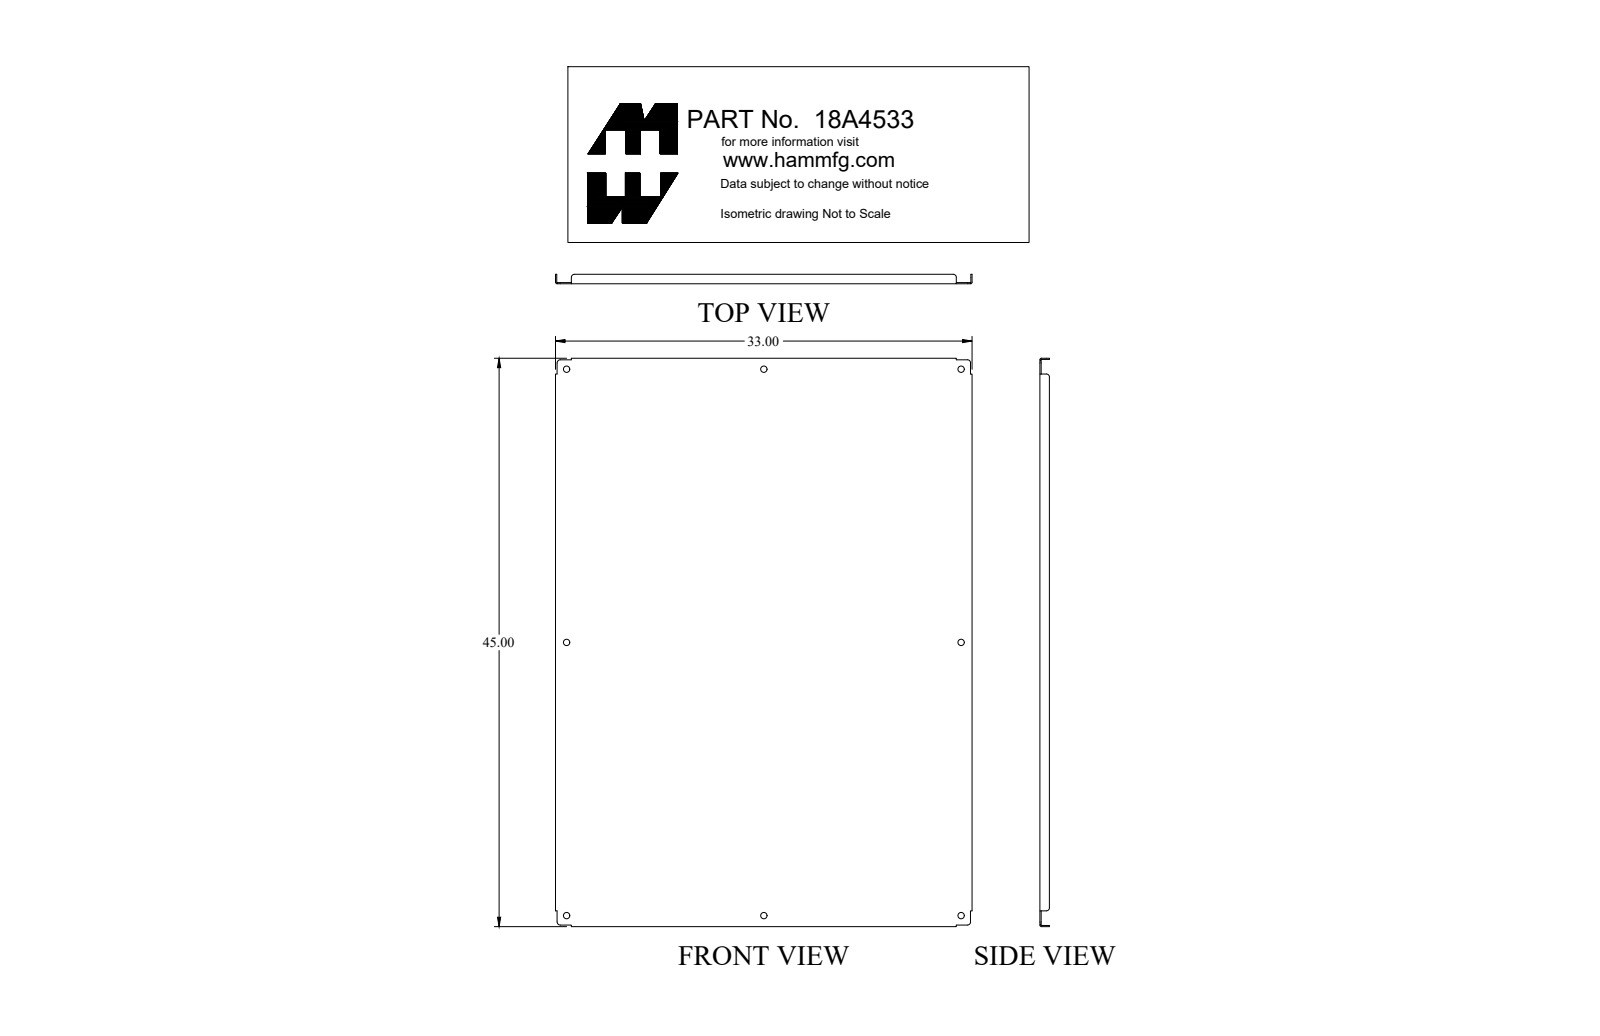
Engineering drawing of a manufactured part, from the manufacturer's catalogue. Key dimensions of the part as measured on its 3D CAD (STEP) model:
Part name (STEP PRODUCT): 18A4533
STEP written by: SolidWorks 2018 (AUTOMOTIVE_DESIGN)
Units: inches
Bodies: 1 solid, 58 faces (30 planar, 28 cylindrical, 0 other)
Overall size (bounding box): 45 × 33 × 0.75
Volume: 149.4 in³ · Surface area: 3 162 in²
Round holes (diameter × count): ⌀0.5 ×8
Partial cylindrical surfaces — rounded edges, fillets, slot ends (radius × count): R0.25 ×8, R0.03 ×4, R0.125 ×4
Main face-to-face distances: 0.095, 32.905, 44.905, 33, 32.81, 45, 44.81, 0.75, 0.655, 0.125
Hole centre spacings: 15.625, 21.625, 26.679, 38.003, 45.985, 31.25, 43.25, 53.358
